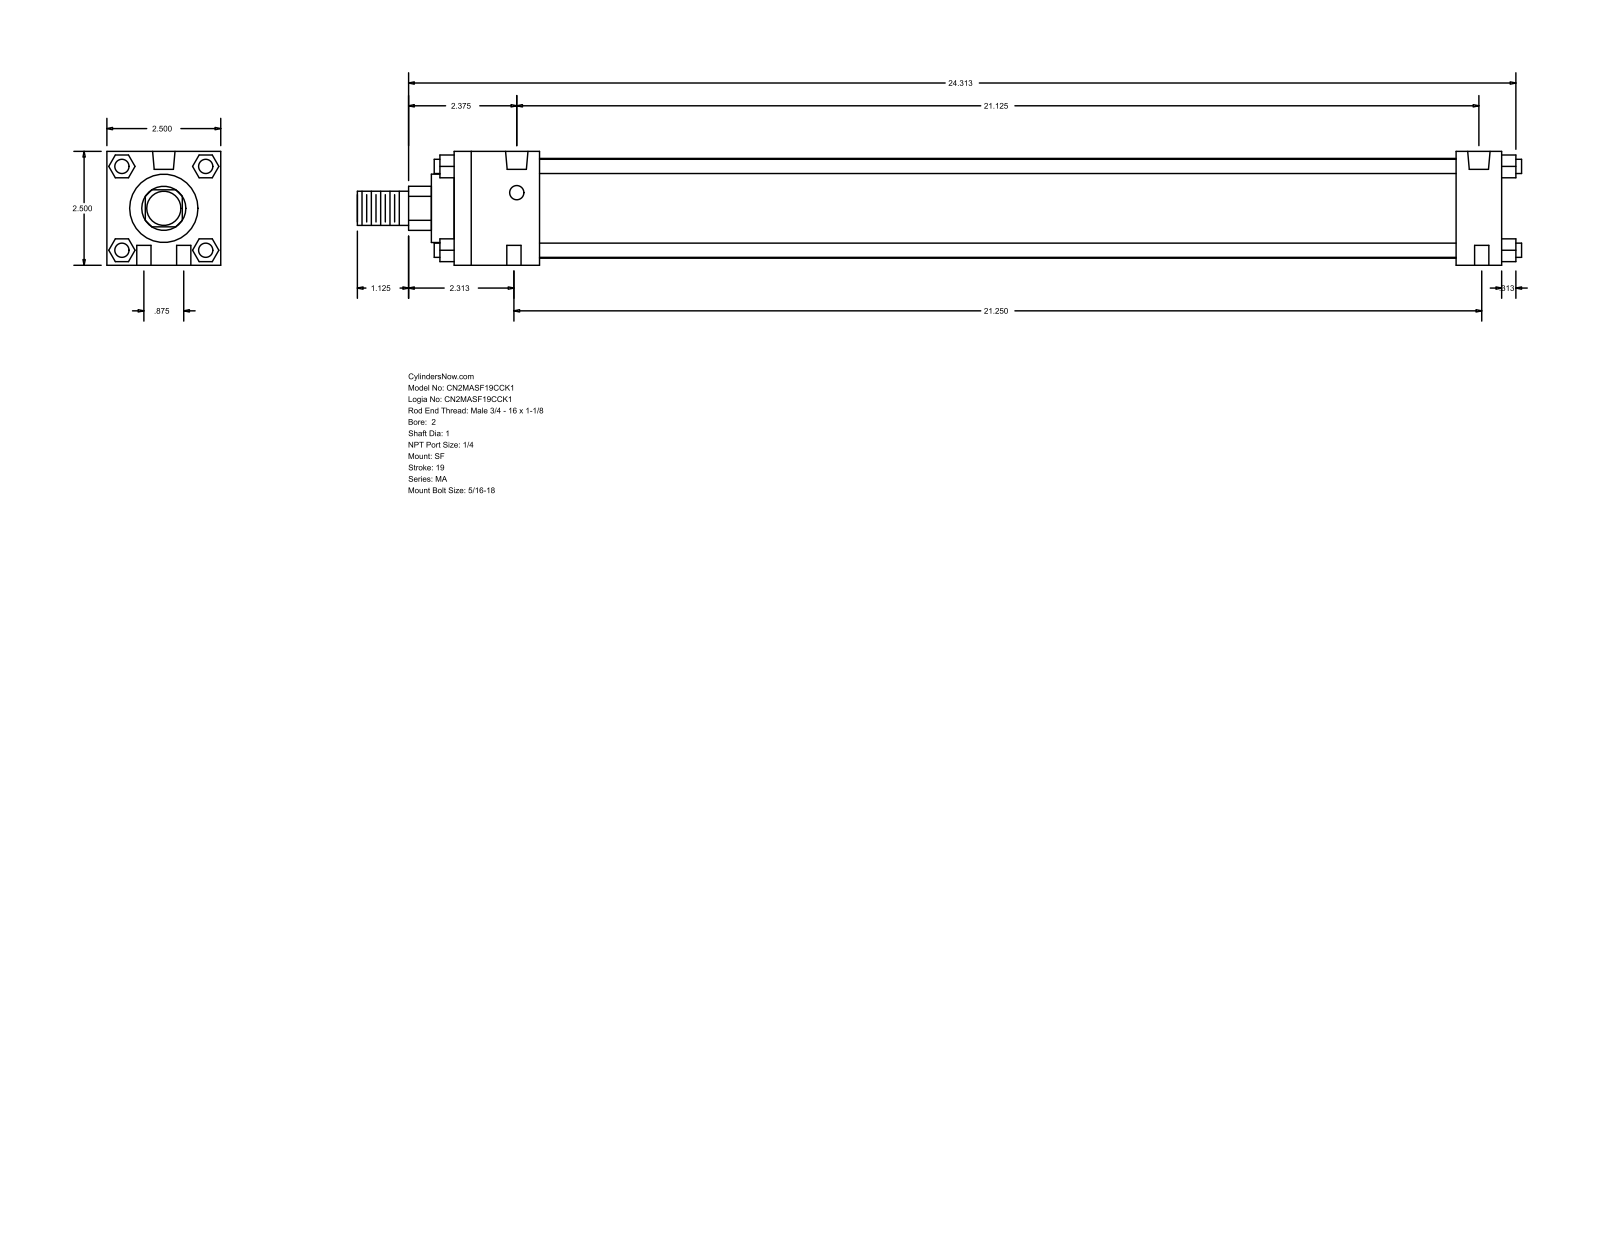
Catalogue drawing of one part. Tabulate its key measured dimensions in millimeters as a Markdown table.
| quantity | value |
| --- | --- |
| part name | MA_SF__0200_1 |
| STEP written by | GSSL Pune (CONFIG_CONTROL_DESIGN) |
| units | millimeters |
| bodies | 0 solids, 124 faces (94 planar, 30 cylindrical, 0 other) |
| overall size | 649.29 × 63.5 × 63.5 |
| round holes (diameter × count) | 7.94 × 6, 12.49 × 2 |
| round bosses / shafts (diameter × count) | 7.94 × 4, 55.63 × 1, 38.1 × 1, 25.4 × 1, 19.05 × 1 |
| partial cylindrical surfaces (radius × count) | 12.29 × 1 |
| main face-to-face distances | 63.5, 584.2, 12.7, 25.4, 558.8, 47.63, 511.17, 536.57, 40.47, 23.37 |
| hole center spacings | 11.22, 538.27, 22.22, 536.57, 539.75, 540.21 |
